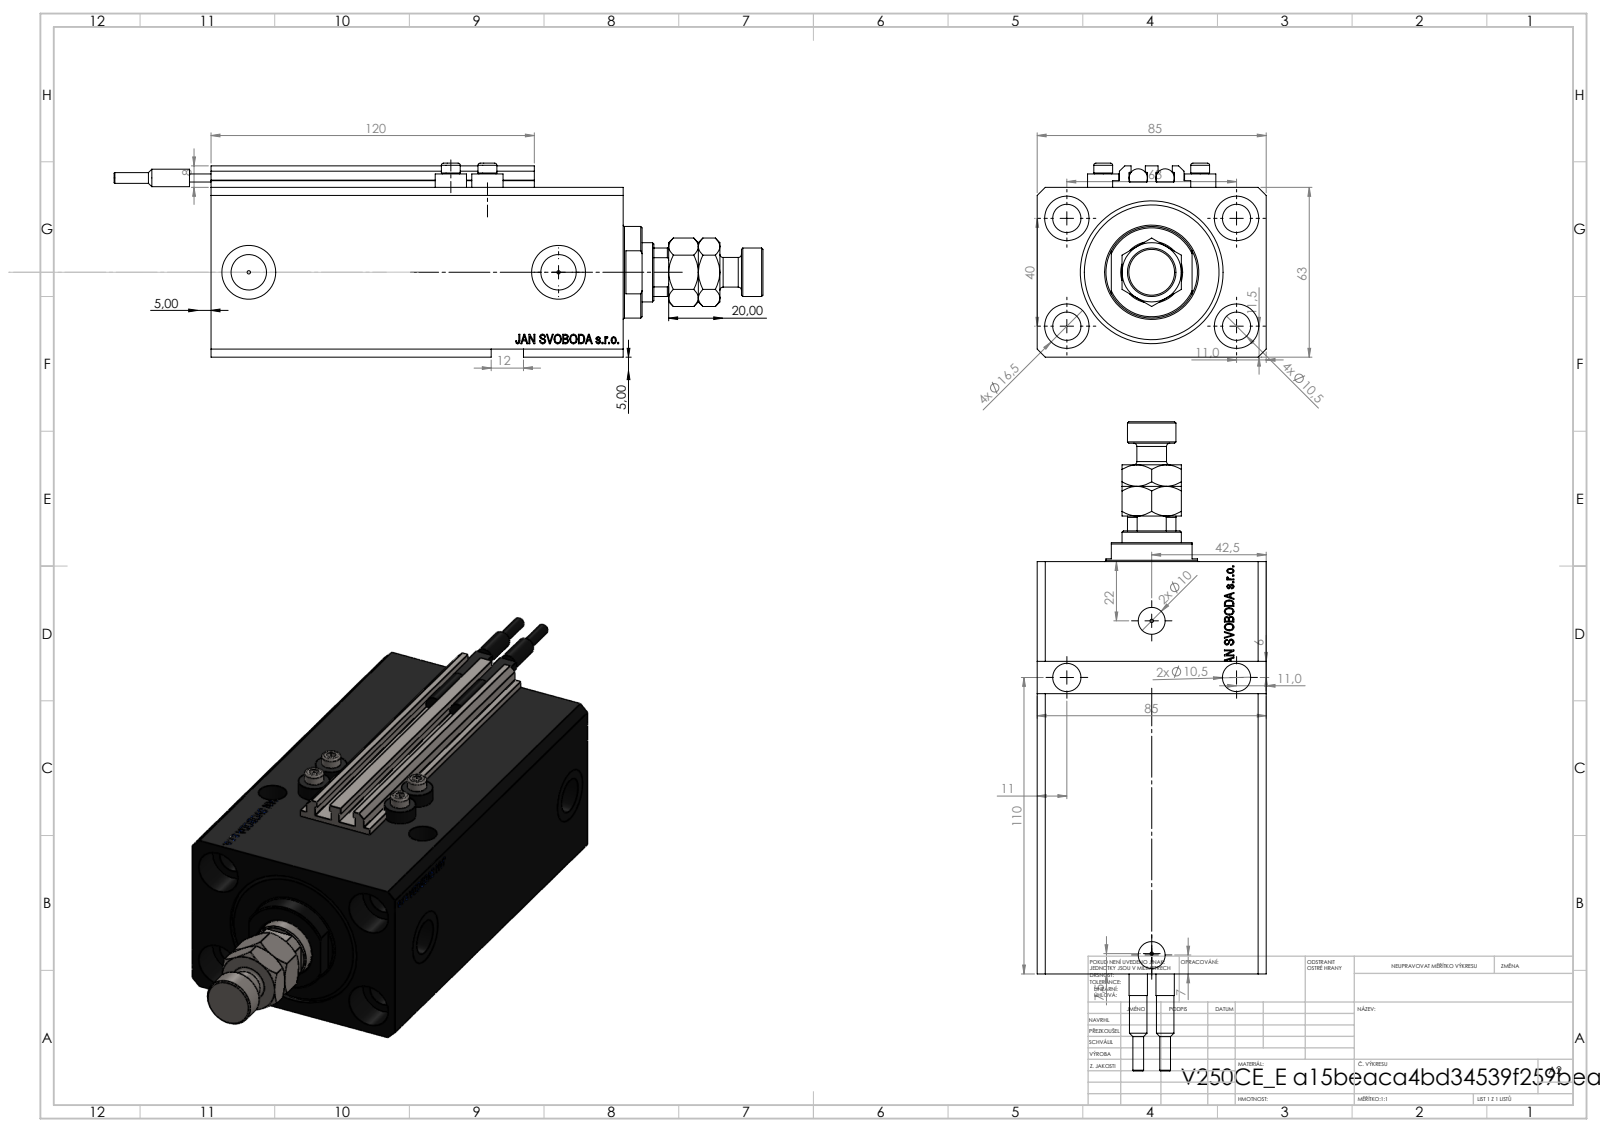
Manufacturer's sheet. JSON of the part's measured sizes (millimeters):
{"part_name": "V250CE_C_VCP; SWITCH_V250CE; MFA; V250CE_VC_E (+2 more)", "step_written_by": "SolidWorks 2019 (CONFIG_CONTROL_DESIGN)", "units": "millimeters", "bodies": {"solids": 11, "faces": 1227, "planar": 587, "cylindrical": 174, "other": 466}, "overall_size": [241, 85, 72], "volume_mm3": 694487, "surface_area_mm2": 147959, "round_holes": [[10.5, 8], [1.25, 4], [4, 4], [16.5, 4], [10, 2], [13.16, 2], [20, 2], [12.5, 1], [22, 1], [40, 1], [53, 1]], "round_bosses_or_shafts": [[11.6, 4], [7, 4], [6.8, 2], [6.5, 2], [4, 2], [34, 1], [18, 1], [11, 1]], "partial_cylinders_radius": [[0.2, 10], [10.5, 1]], "face_to_face_distances": [63, 85, 17, 153, 136, 65, 11.4, 124.6, 141.6, 3], "hole_center_spacings": [37.31, 63, 13.6, 15.4, 24.96, 33.62, 36, 37.86]}
